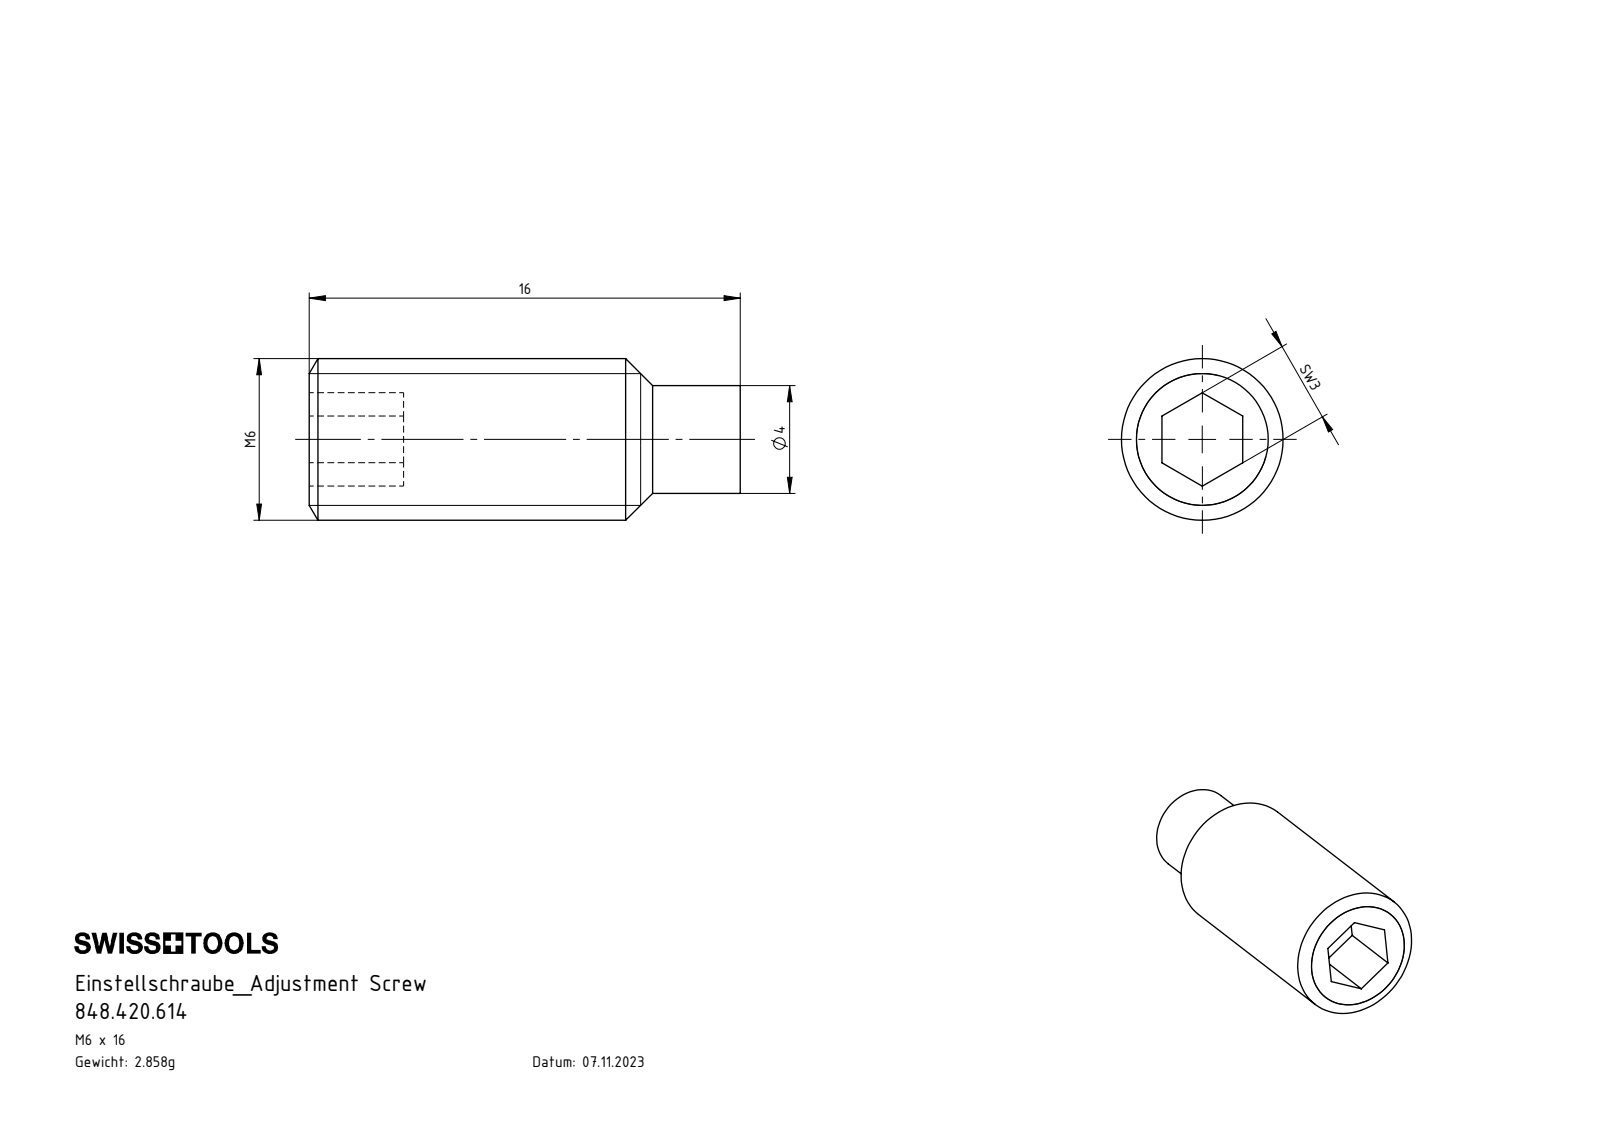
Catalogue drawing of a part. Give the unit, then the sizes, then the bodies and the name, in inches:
Units: inches
Overall size (bounding box): 0.63 × 0.236 × 0.236
Round bosses / shafts (diameter × count): ⌀0.236 ×1, ⌀0.157 ×1
Main face-to-face distances: 0.118, 0.63, 0.138, 0.492
Volume: 0.022 in³ · Surface area: 0.553 in²
Bodies: 1 solid, 17 faces (9 planar, 4 cylindrical, 4 other)
Part name (STEP PRODUCT): 848.420.614
STEP written by: SolidWorks 2022 (AUTOMOTIVE_DESIGN)
